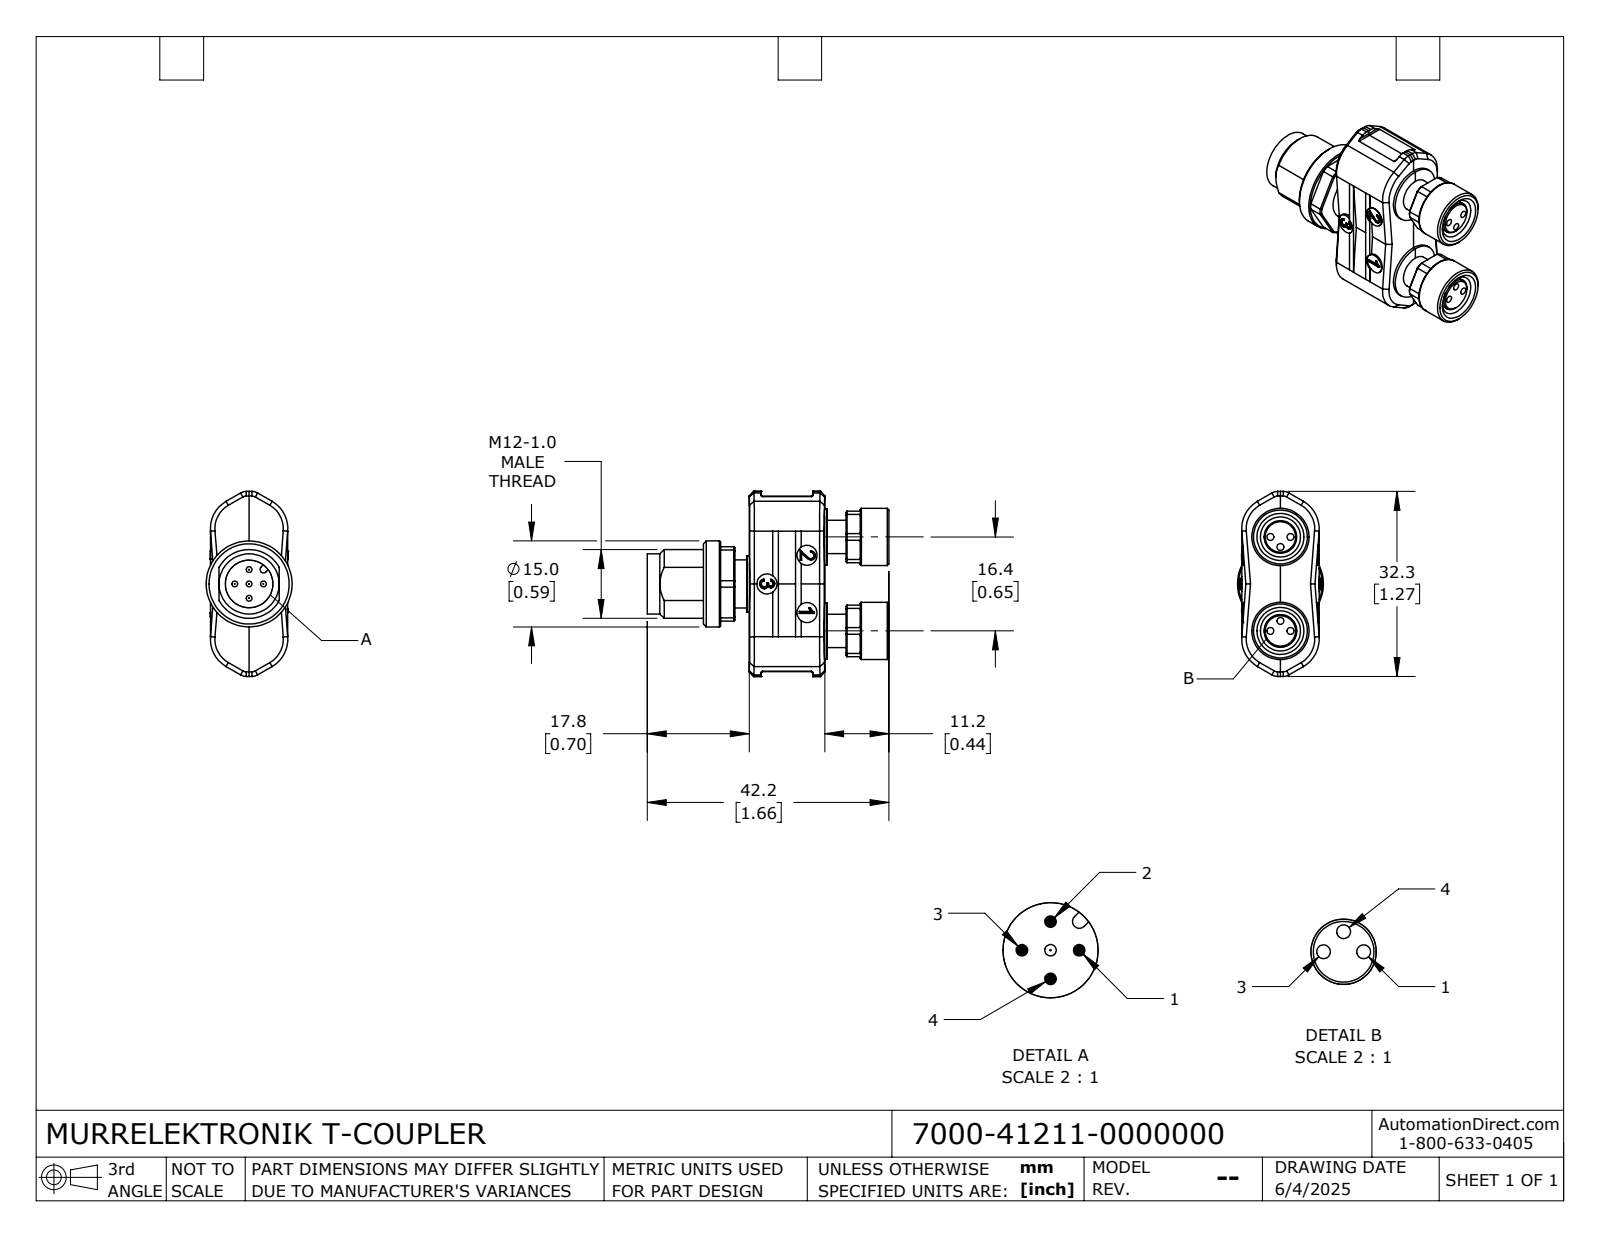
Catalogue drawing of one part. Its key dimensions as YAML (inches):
part_name: "7000-41211-0000000"
step_written_by: "SolidWorks 2024 (CONFIG_CONTROL_DESIGN)"
units: inches
bodies: {solids: 1, faces: 498, planar: 250, cylindrical: 111, other: 137}
overall_size: [1.661, 1.272, 0.591]
volume: 0.464
surface_area: 6.78
round_holes:
  - {diameter: 0.047, count: 6}
  - {diameter: 0.276, count: 2}
  - {diameter: 0.327, count: 1}
round_bosses_or_shafts:
  - {diameter: 0.039, count: 5}
  - {diameter: 0.386, count: 3}
  - {diameter: 0.138, count: 3}
  - {diameter: 0.394, count: 2}
  - {diameter: 0.228, count: 2}
  - {diameter: 0.224, count: 2}
  - {diameter: 0.591, count: 1}
  - {diameter: 0.413, count: 1}
partial_cylinders:
  - {radius: 0.008, count: 4}
  - {radius: 0.079, count: 4}
  - {radius: 0.217, count: 4}
  - {radius: 0.035, count: 2}
  - {radius: 0.024, count: 1}
  - {radius: 0.236, count: 1}
  - {radius: 0.283, count: 1}
face_to_face_distances: [0.52, 0.473, 0.018, 0.537, 0.059, 0.764, 0.472, 0.354, 0.035, 0.512]
hole_center_spacings: [0.069, 0.097, 0.33, 0.581, 0.649, 0.646, 0.138, 0.254]
